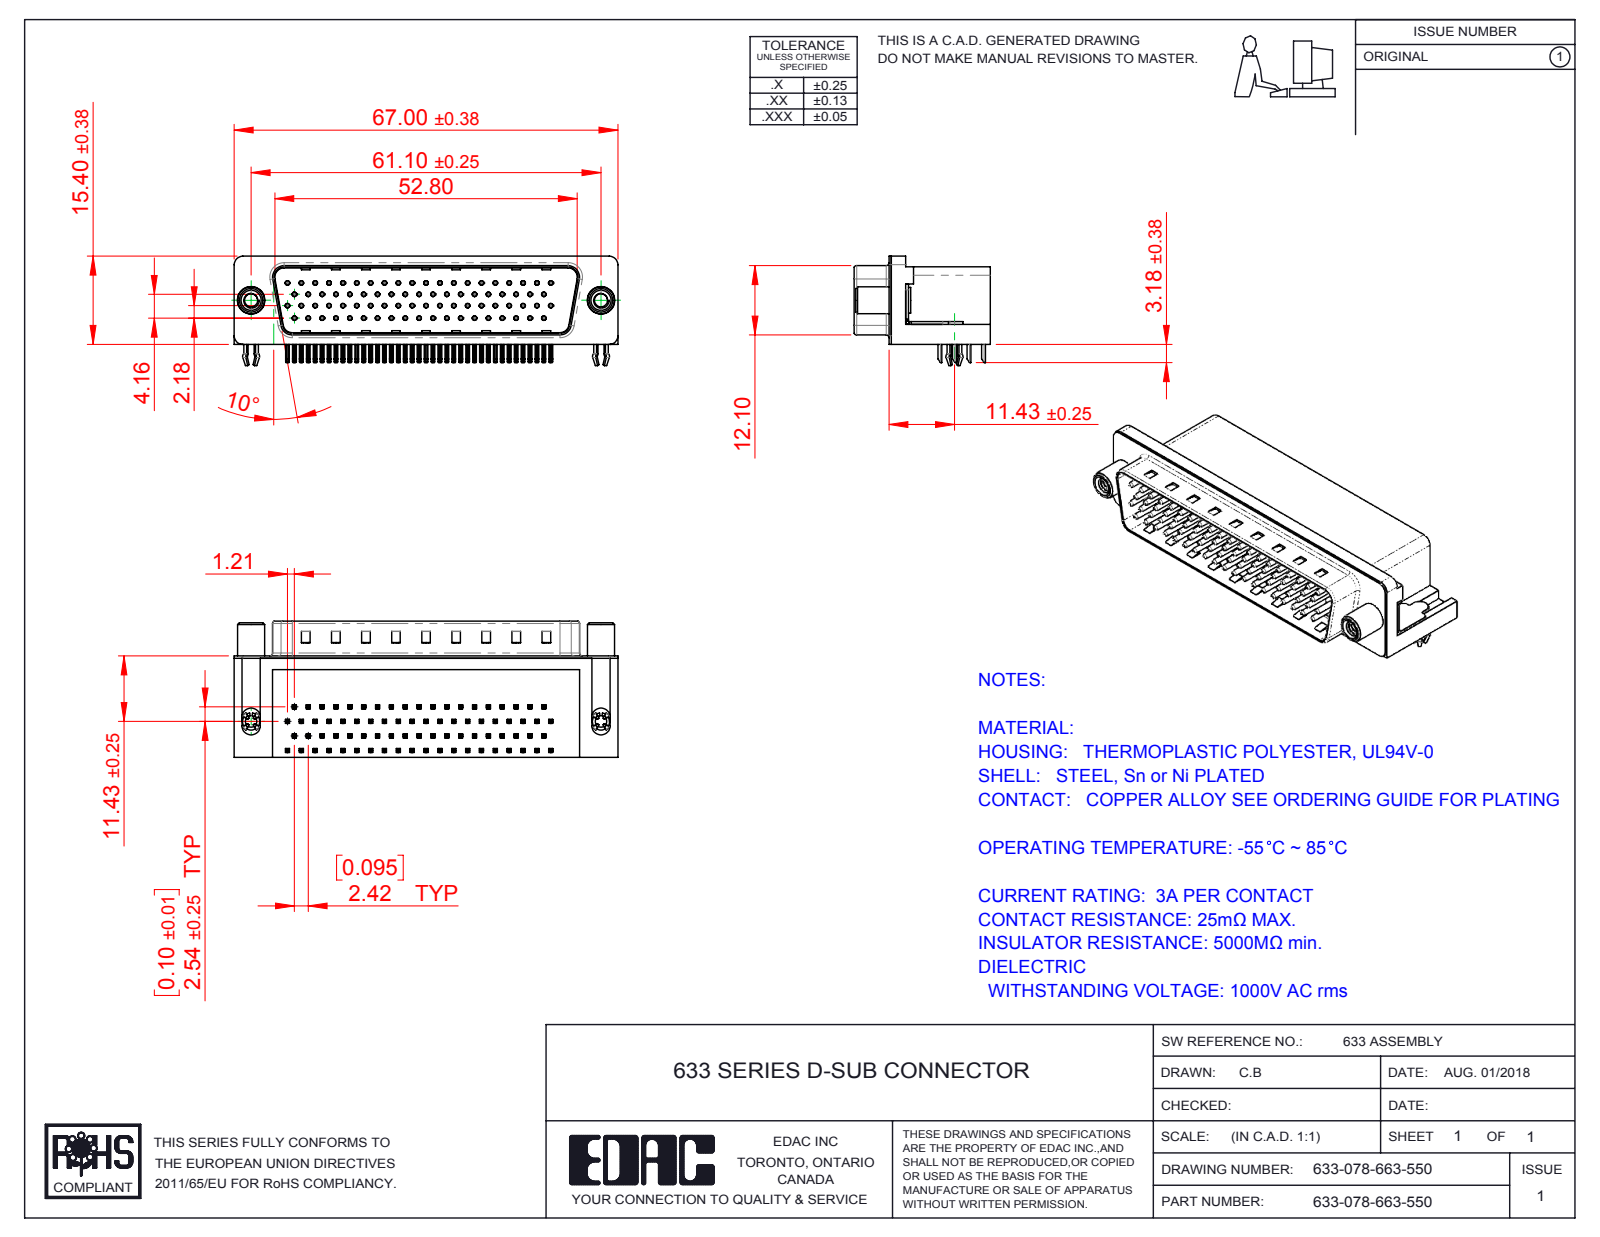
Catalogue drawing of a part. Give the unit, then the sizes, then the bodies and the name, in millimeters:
Units: millimetres
Overall size (bounding box): 67 × 23.8 × 19.1
Round holes (diameter × count): ⌀0.35 ×78, ⌀0.8 ×78, ⌀2 ×2, ⌀2.3 ×2, ⌀3.1 ×2, ⌀4 ×2, ⌀4.8 ×2, ⌀5 ×2
Round bosses / shafts (diameter × count): ⌀0.75 ×78, ⌀4.9 ×2, ⌀4.7 ×2, ⌀4.5 ×2, ⌀3.85 ×2, ⌀3 ×2
Partial cylindrical surfaces — rounded edges, fillets, slot ends (radius × count): R0.25 ×316, R0.12 ×156, R1 ×16, R0.5 ×9, R1.6 ×8, R1.5 ×6, R0.45 ×4, R0.9 ×4
Main face-to-face distances: 0.4, 13.2, 17.3, 11.7, 13.35, 2.05, 13.75, 1.65, 1.85, 11.9
Hole centre spacings: 2.42, 4.84, 7.26, 9.68, 6.26, 7.13, 12.1, 8.62
Volume: 14 713 mm³ · Surface area: 16 628 mm²
Bodies: 84 solids, 6390 faces (4015 planar, 1792 cylindrical, 583 other)
Part name (STEP PRODUCT): 633-078-663-550; 633 Shell_78 Contact; 633 Contact Middle_78 Contact; 633 Contact Top 78 (+5 more)
STEP written by: SolidWorks 2016 (CONFIG_CONTROL_DESIGN)
